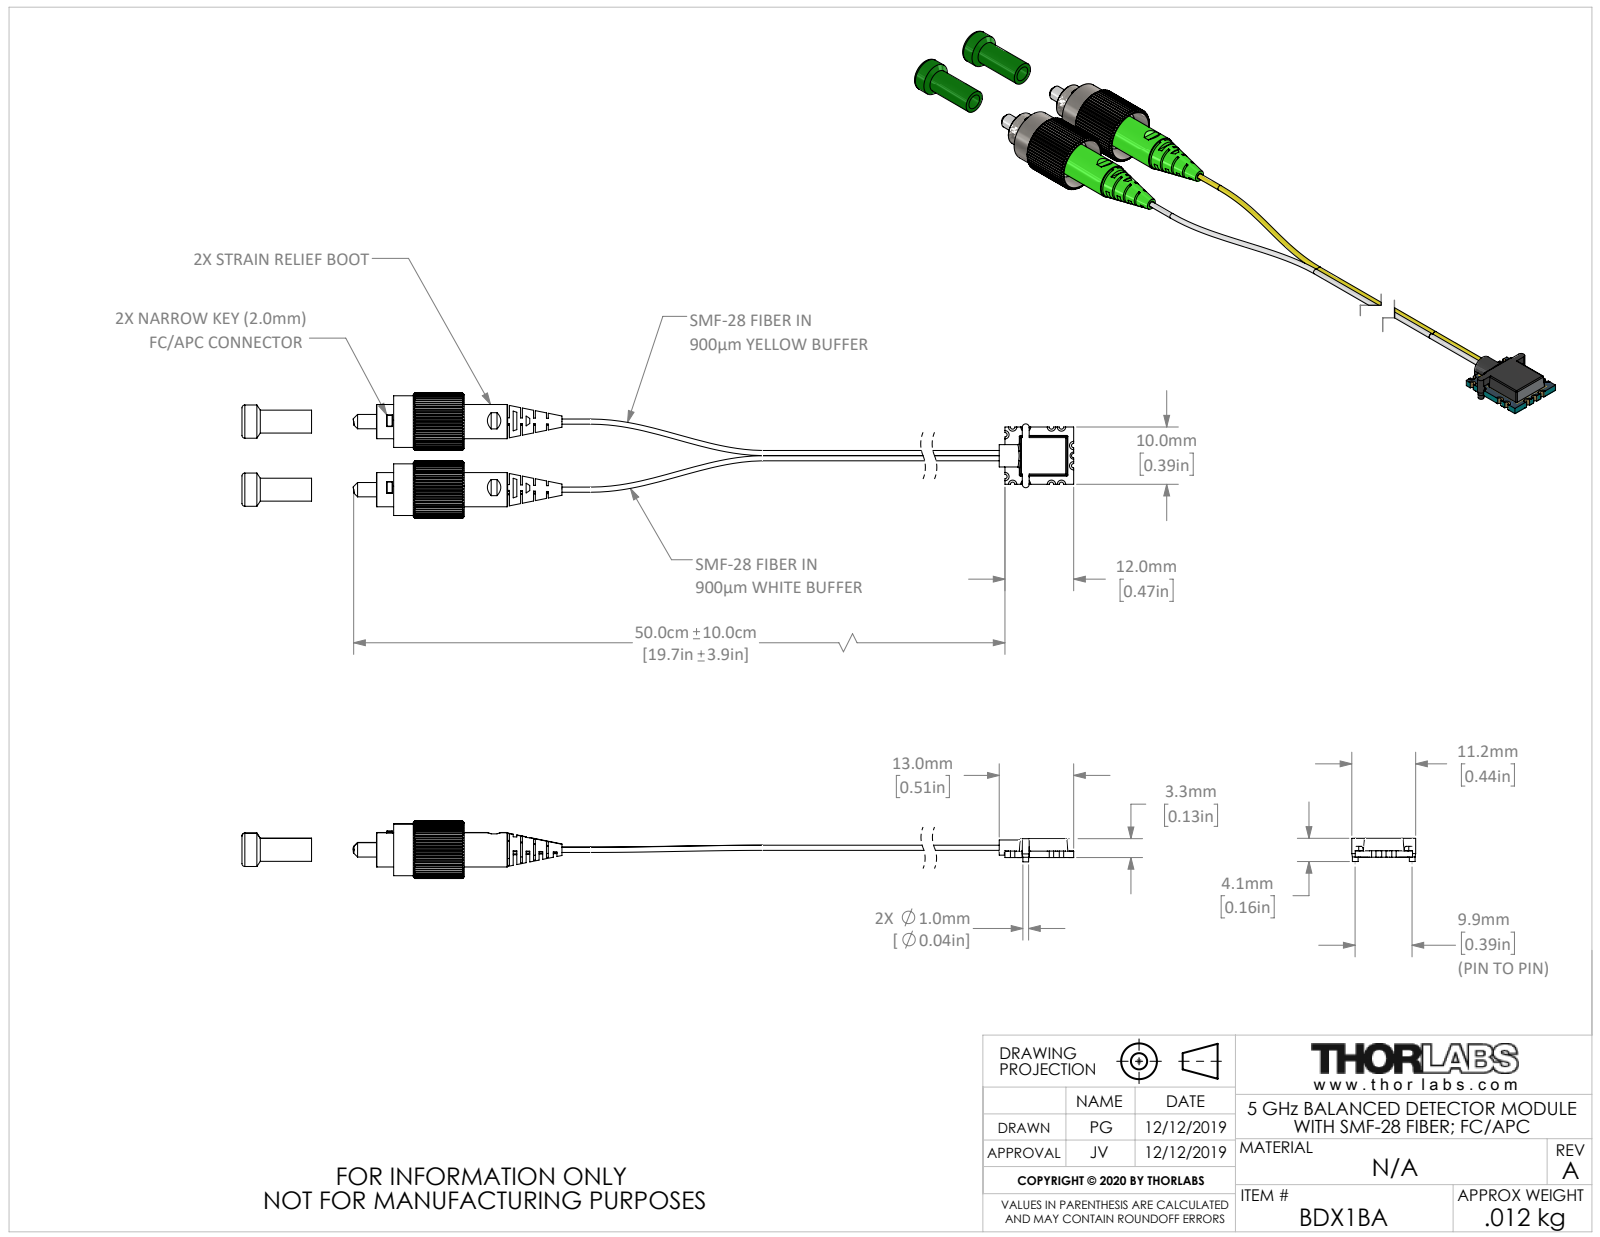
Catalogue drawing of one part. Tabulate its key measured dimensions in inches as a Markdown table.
| quantity | value |
| --- | --- |
| part name | BDX1BA |
| STEP written by | SolidWorks 2018 (AUTOMOTIVE_DESIGN) |
| units | inches |
| bodies | 14 solids, 903 faces (521 planar, 299 cylindrical, 83 other) |
| overall size | 7.193 × 0.862 × 0.394 |
| volume | 0.134 in³ |
| surface area | 9.682 in² |
| round holes (diameter × count) | 0.055 × 2, 0.104 × 2, 0.118 × 2, 0.12 × 2, 0.155 × 2, 0.175 × 2, 0.2 × 2, 0.325 × 2, 0.355 × 2, 0.028 × 1 |
| round bosses / shafts (diameter × count) | 0.035 × 4, 0.28 × 2, 0.235 × 2, 0.228 × 2, 0.195 × 2, 0.157 × 2, 0.15 × 2, 0.14 × 2 |
| partial cylindrical surfaces (radius × count) | 0.015 × 11, 0.008 × 10, 0.029 × 10, 0.011 × 8, 0.025 × 3, 0.012 × 2, 0.025 × 2, 0.034 × 2 |
| main face-to-face distances | 0.267, 0.267, 0.044, 0.062, 0.04, 0.02, 0.102, 0.089, 0.013, 0.13 |
| hole center spacings | 0.469 |
